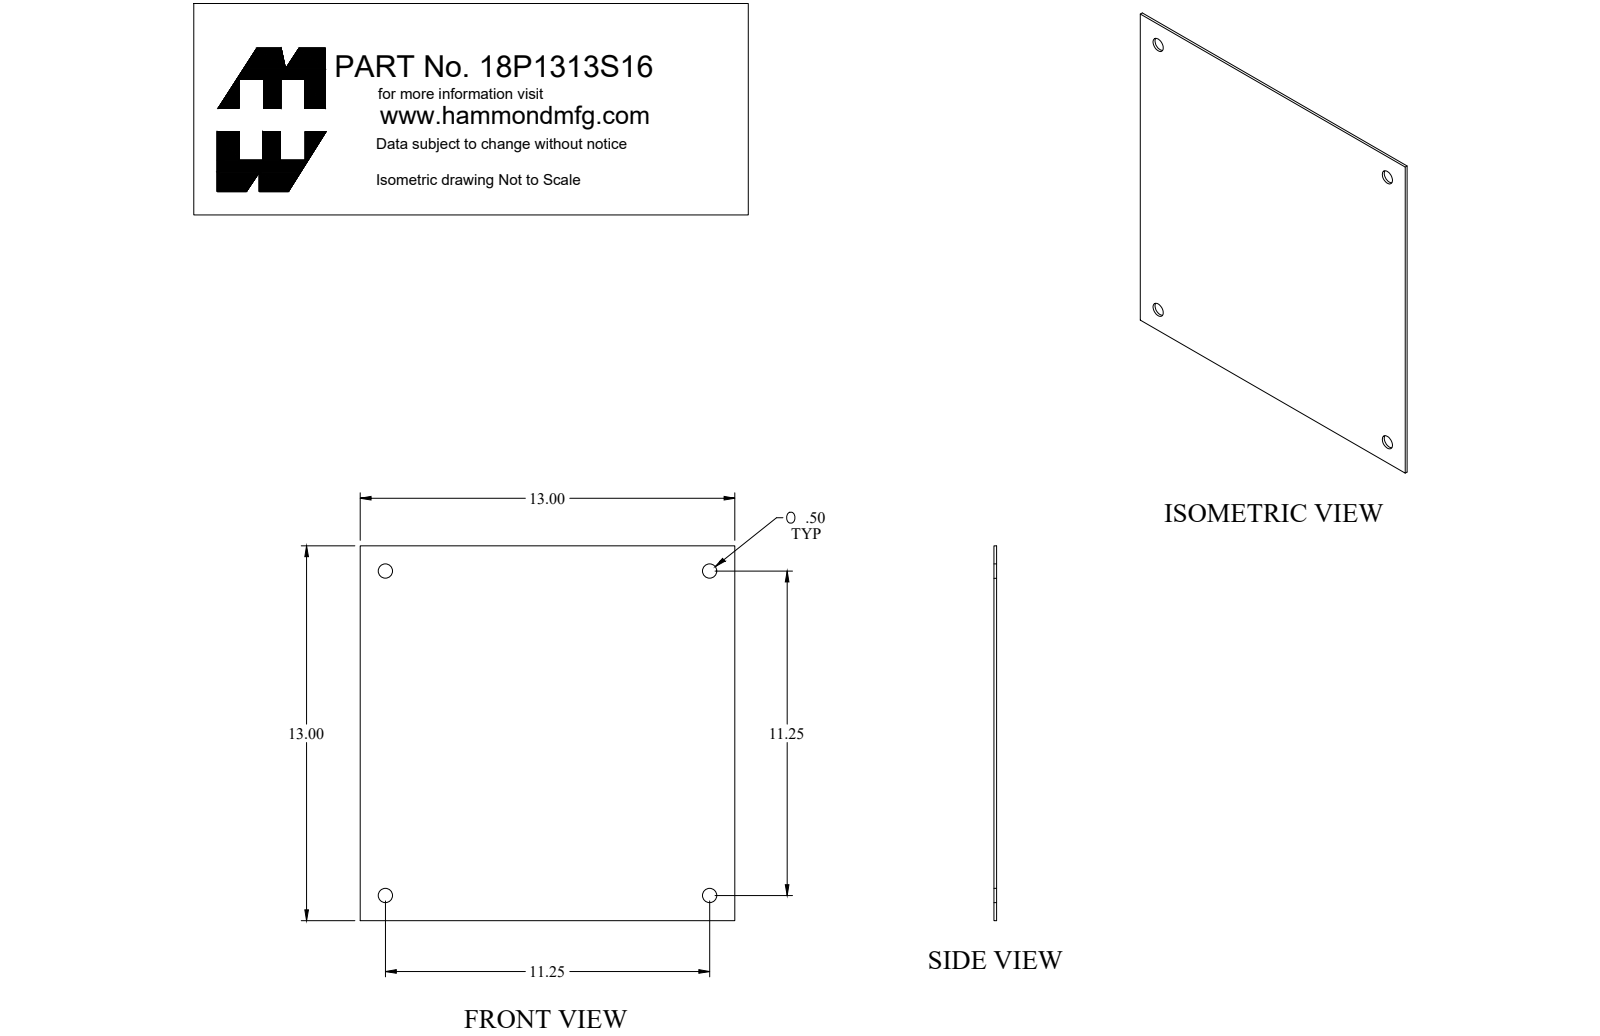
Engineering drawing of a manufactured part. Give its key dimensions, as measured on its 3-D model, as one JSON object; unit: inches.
{"part_name": "18P1313S16_Default", "step_written_by": "SolidWorks 2018 (CONFIG_CONTROL_DESIGN)", "units": "inches", "bodies": {"solids": 1, "faces": 14, "planar": 6, "cylindrical": 8, "other": 0}, "overall_size": [13, 13, 0.095], "volume_in3": 15.98, "surface_area_in2": 342, "round_holes": [[0.5, 4]], "face_to_face_distances": [0.095, 13], "hole_center_spacings": [11.25, 15.911]}
